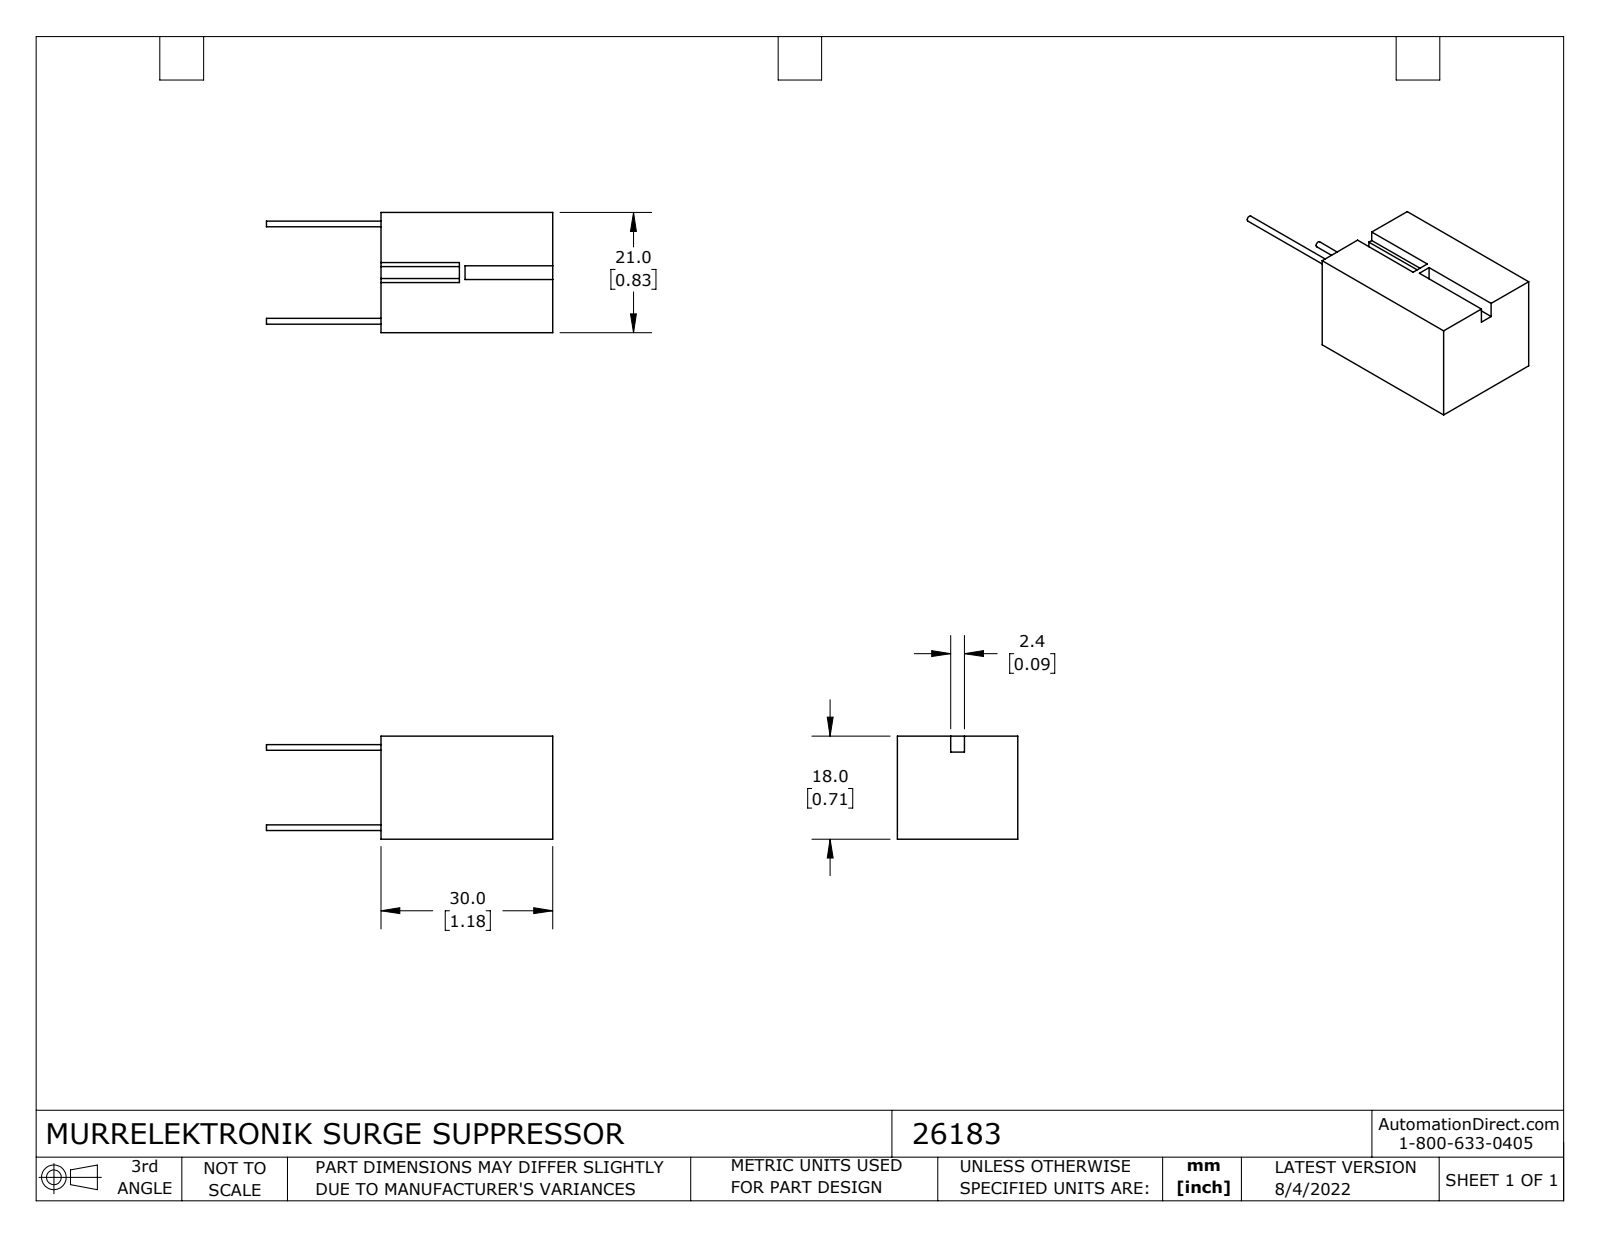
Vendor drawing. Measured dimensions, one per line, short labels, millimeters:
name: 26183
written by: SolidWorks 2021 (CONFIG_CONTROL_DESIGN)
unit: mm
bodies: 1 solid, 24 faces (20 planar, 4 cylindrical, 0 other)
size: 50 × 21 × 18
volume: 11 154 mm³; area: 3 384 mm²
bosses: 2× ⌀1
face distances: 18, 21, 30, 2.8, 9.3, 11.7, 15.2, 8.75, 12.25, 0.55
